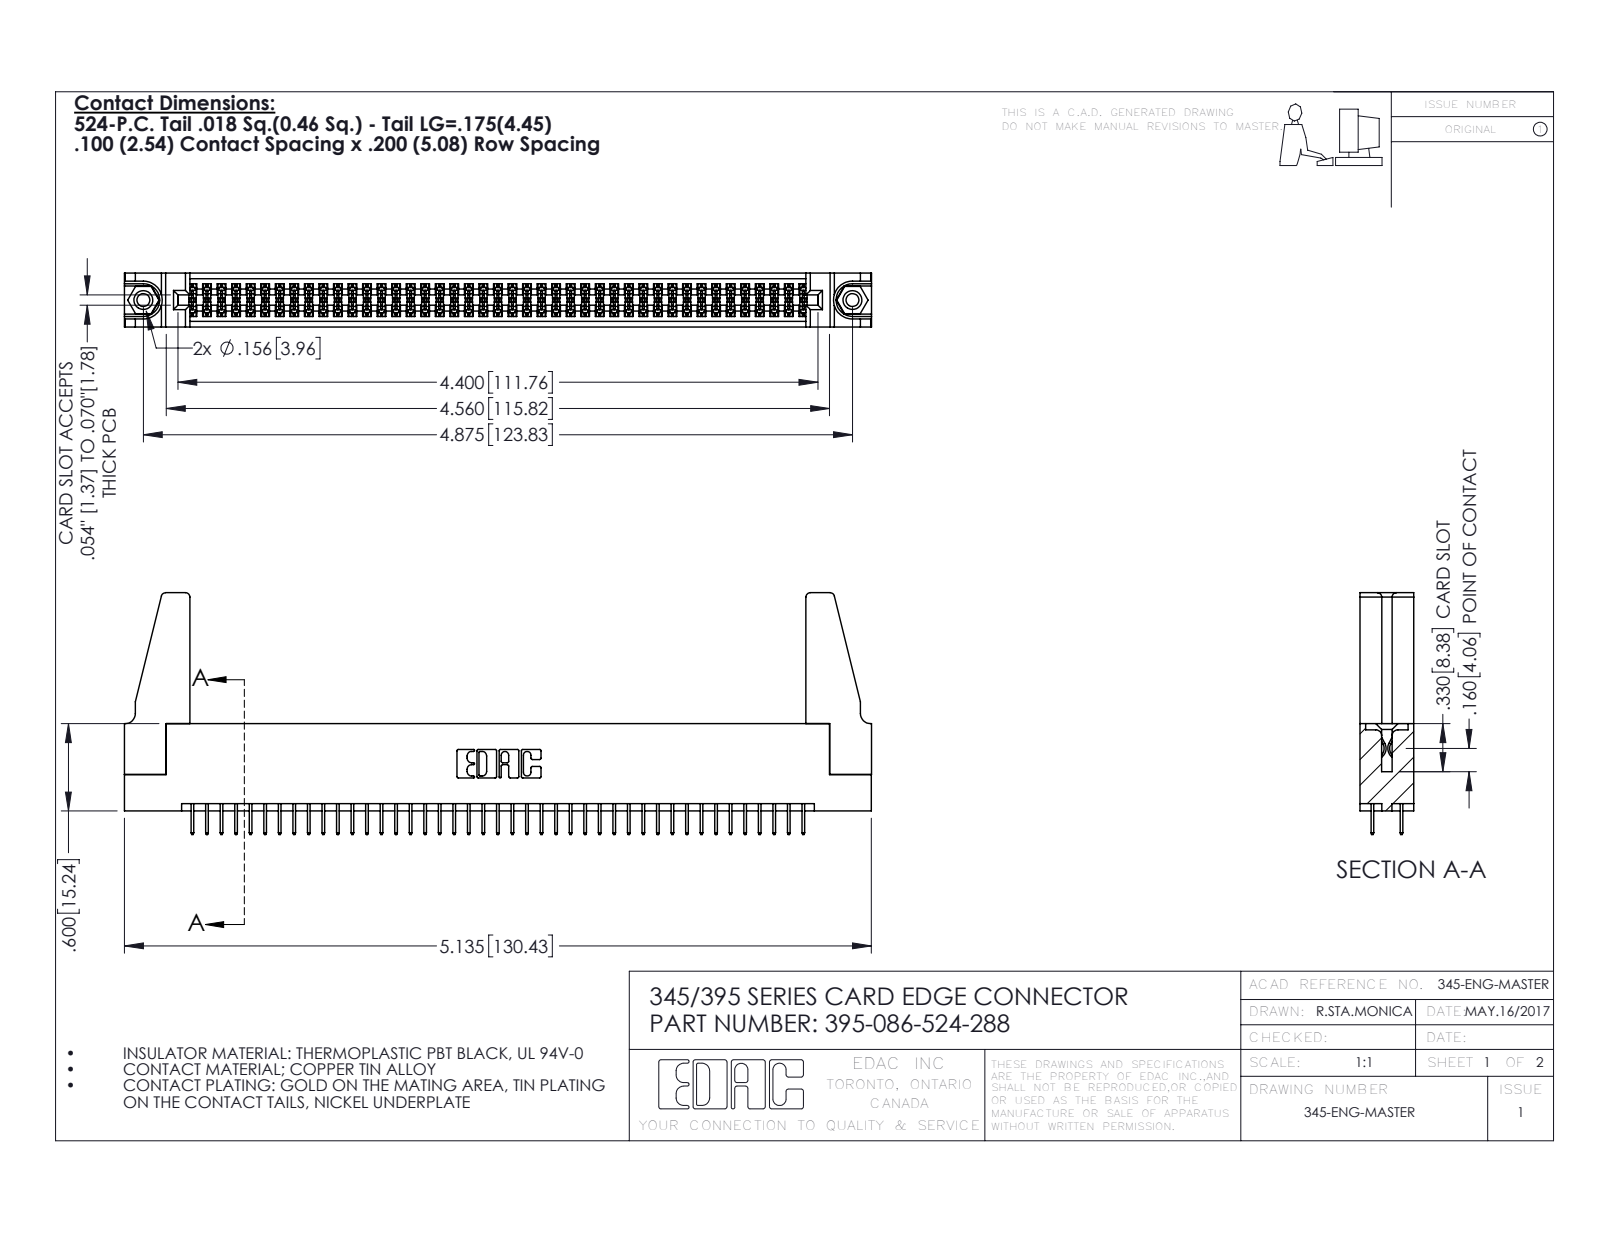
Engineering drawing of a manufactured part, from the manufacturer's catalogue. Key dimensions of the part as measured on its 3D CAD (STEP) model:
Part name (STEP PRODUCT): 345 Part_Flush Mounting Lugs - 0.156 Dia-TH; 345-250-001_345-250-001-102; 395-086-524-288; 345-220-078_345-220-088 (+1 more)
STEP written by: SolidWorks 2016 (CONFIG_CONTROL_DESIGN)
Units: inches
Bodies: 91 solids, 4894 faces (3506 planar, 1372 cylindrical, 16 other)
Overall size (bounding box): 5.136 × 1.662 × 0.37
Volume: 0.964 in³ · Surface area: 33.09 in²
Round holes (diameter × count): ⌀0.089 ×2, ⌀0.125 ×2, ⌀0.156 ×2, ⌀0.064 ×1
Round bosses / shafts (diameter × count): ⌀0.155 ×2
Partial cylindrical surfaces — rounded edges, fillets, slot ends (radius × count): R0.006 ×129, R0.01 ×22, R0.03 ×8, R0.007 ×6, R0.031 ×6, R0.026 ×3, R0.014 ×2, R0.019 ×2
Main face-to-face distances: 0.072, 0.298, 0.37, 0.2, 0.098, 0.272, 0.025, 0.225, 0.072, 0.175
Hole centre spacings: 0.27, 4.639, 4.875
